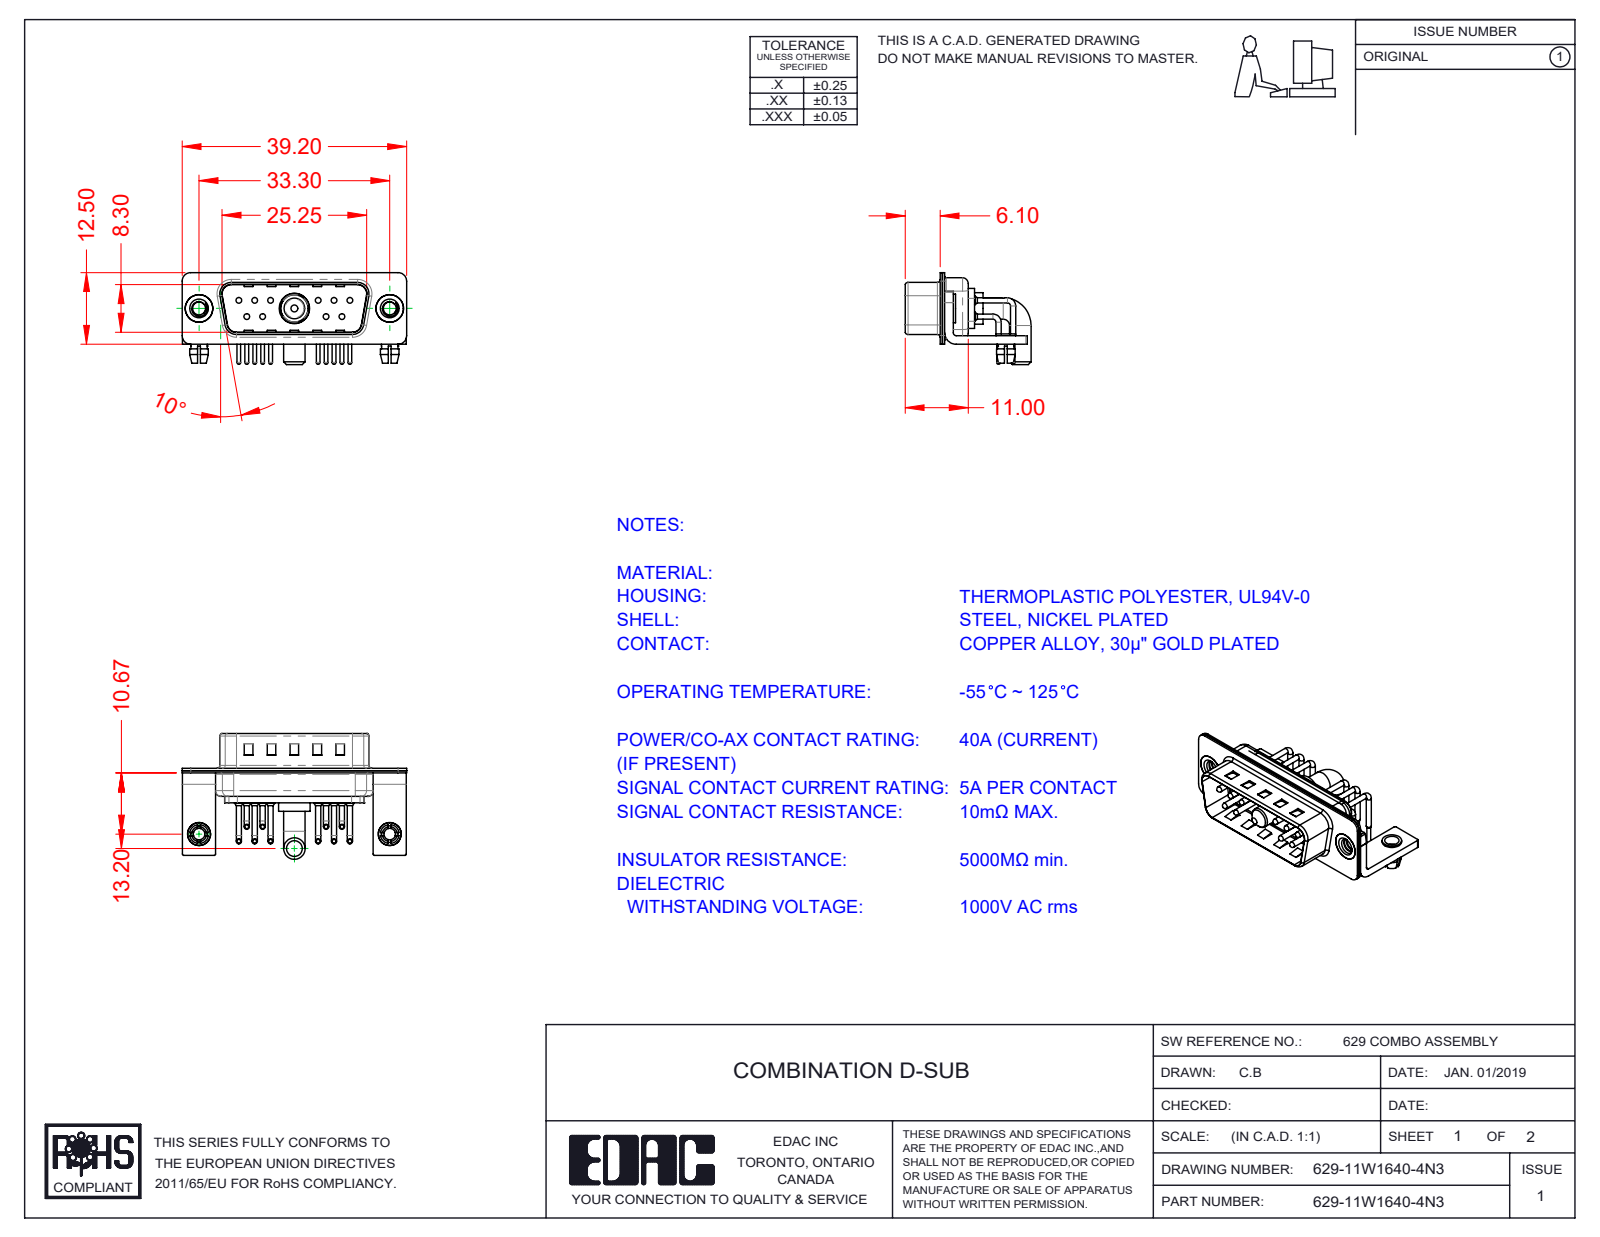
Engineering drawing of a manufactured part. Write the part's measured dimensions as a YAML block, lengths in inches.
part_name: "629Combo Shell Rear_15 Contacts; 629Combo Board Lock; 629Combo Shell Front_15 Contacts; 629Combo Threaded Rivet_3 (+6 more)"
step_written_by: "SolidWorks 2020 (CONFIG_CONTROL_DESIGN)"
units: inches
bodies: {solids: 21, faces: 1628, planar: 866, cylindrical: 568, other: 194}
overall_size: [1.543, 0.865, 0.632]
volume: 0.149
surface_area: 9.415
round_holes:
  - {diameter: 0.079, count: 12}
  - {diameter: 0.03, count: 10}
  - {diameter: 0.063, count: 10}
  - {diameter: 0.089, count: 2}
  - {diameter: 0.098, count: 2}
  - {diameter: 0.126, count: 2}
  - {diameter: 0.157, count: 2}
  - {diameter: 0.189, count: 2}
  - {diameter: 0.191, count: 1}
  - {diameter: 0.209, count: 1}
round_bosses_or_shafts:
  - {diameter: 0.035, count: 20}
  - {diameter: 0.059, count: 10}
  - {diameter: 0.039, count: 10}
  - {diameter: 0.026, count: 10}
  - {diameter: 0.197, count: 2}
  - {diameter: 0.193, count: 2}
  - {diameter: 0.157, count: 2}
  - {diameter: 0.148, count: 2}
partial_cylinders:
  - {radius: 0.01, count: 16}
  - {radius: 0.059, count: 16}
  - {radius: 0.079, count: 13}
  - {radius: 0.04, count: 10}
  - {radius: 0.02, count: 9}
  - {radius: 0.063, count: 8}
  - {radius: 0.039, count: 7}
  - {radius: 0.024, count: 4}
face_to_face_distances: [0.016, 0.031, 0.059, 0.374, 0.358, 0.343, 0.39, 0.024, 0.075, 0.083]
hole_center_spacings: [0.124, 0.109, 0.545, 0.436, 0.654, 0.198, 0.198, 0.218]
